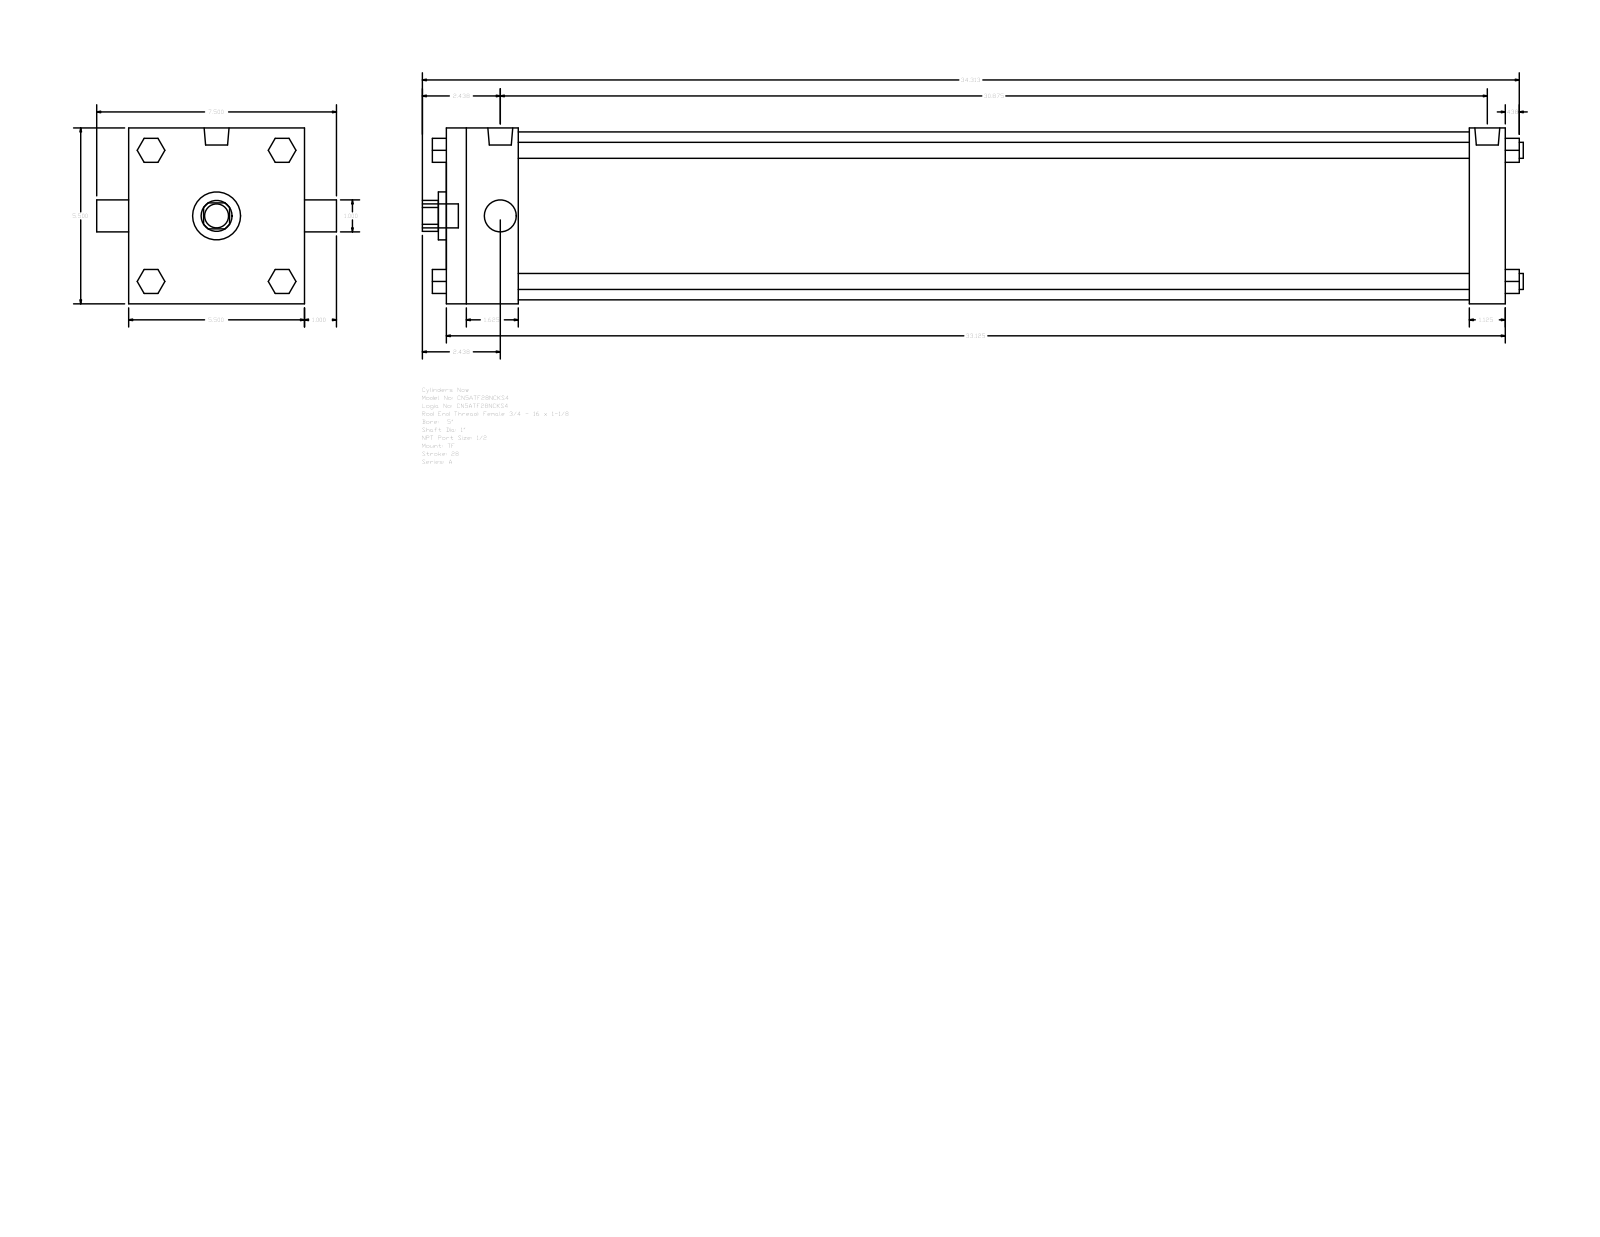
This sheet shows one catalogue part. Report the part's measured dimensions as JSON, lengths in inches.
{"part_name": "A_TF__0500_1", "step_written_by": "GSSL Pune (CONFIG_CONTROL_DESIGN)", "units": "inches", "bodies": {"solids": 0, "faces": 120, "planar": 92, "cylindrical": 28, "other": 0}, "overall_size": [34.437, 7.5, 5.5], "round_holes": [[1, 2], [1.5, 1], [5.25, 1]], "round_bosses_or_shafts": [[0.5, 4], [0.344, 3], [0.778, 2], [0.75, 1]], "partial_cylinders_radius": [[0.484, 1]], "face_to_face_distances": [5.5, 33.125, 1.125, 32, 2.25, 29.75, 30.875, 0.75, 2.05, 3.55]}
